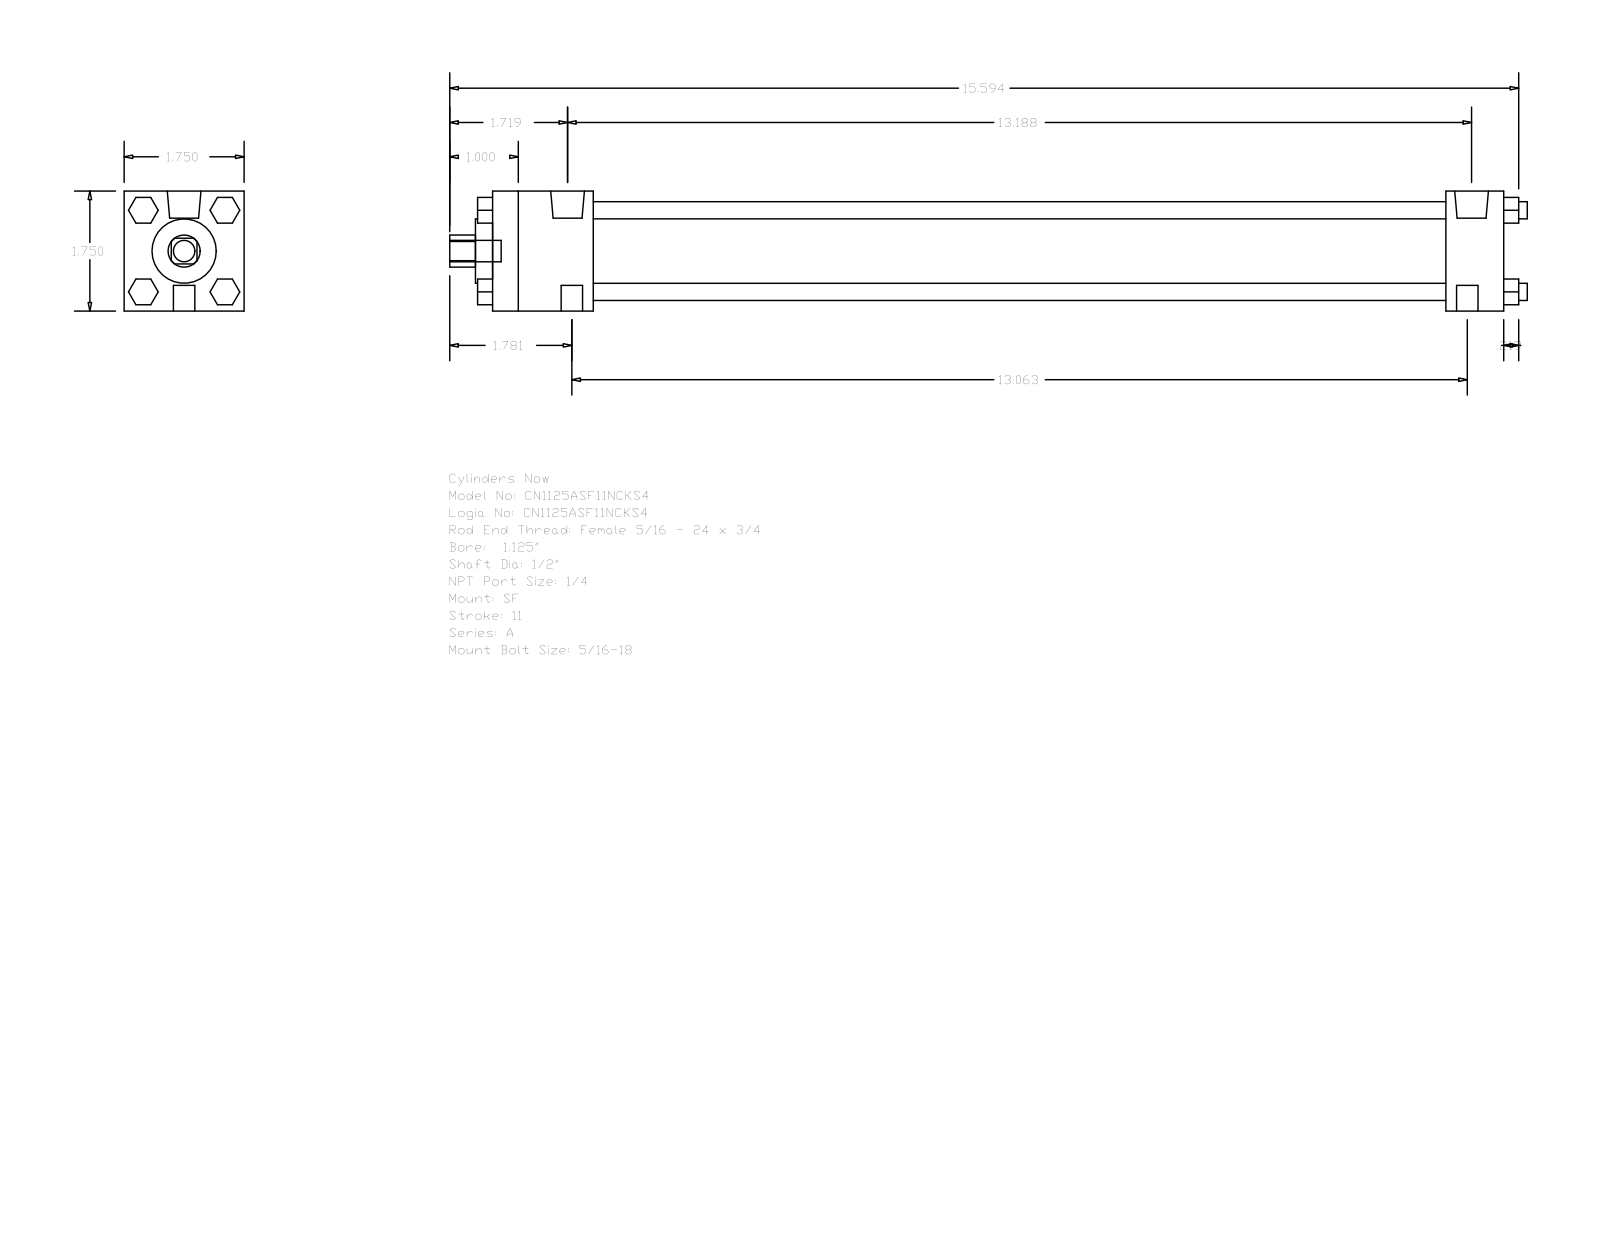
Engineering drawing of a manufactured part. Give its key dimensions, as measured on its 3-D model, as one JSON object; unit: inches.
{"part_name": "A_SF__0112_0.5", "step_written_by": "GSSL Pune (CONFIG_CONTROL_DESIGN)", "units": "inches", "bodies": {"solids": 0, "faces": 120, "planar": 92, "cylindrical": 28, "other": 0}, "overall_size": [15.719, 1.75, 1.75], "round_holes": [[0.5, 1], [0.937, 1], [1.255, 1]], "round_bosses_or_shafts": [[0.25, 4], [0.313, 3], [0.492, 2], [0.219, 2]], "partial_cylinders_radius": [[0.234, 1]], "face_to_face_distances": [1.75, 14.75, 13.906, 0.844, 1.469, 12.437, 13.281, 0.375, 0.22, 0.375]}
